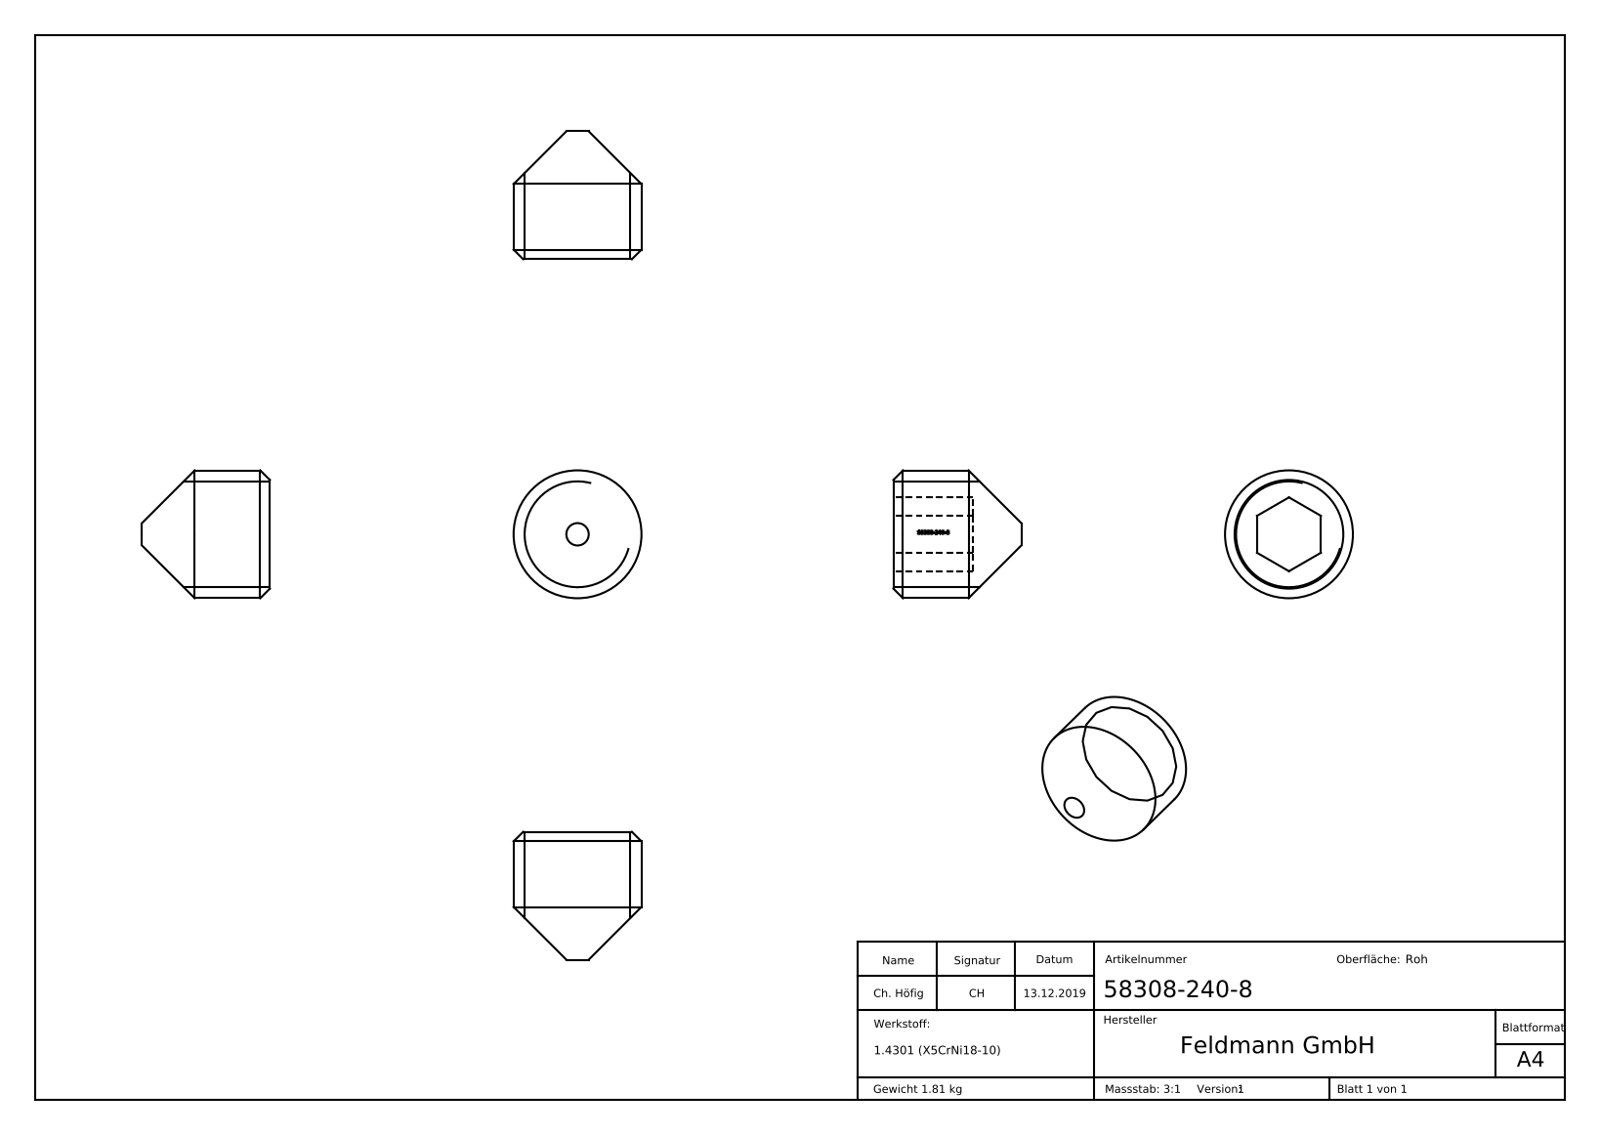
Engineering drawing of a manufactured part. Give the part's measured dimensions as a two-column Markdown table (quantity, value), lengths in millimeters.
| quantity | value |
| --- | --- |
| part name | 58308-240-8 |
| STEP written by | SolidWorks 2015 (CONFIG_CONTROL_DESIGN) |
| units | millimeters |
| bodies | 1 solid, 168 faces (65 planar, 1 cylindrical, 102 other) |
| overall size | 70 × 8 × 8 |
| volume | 229 mm³ |
| surface area | 300 mm² |
| round bosses / shafts (diameter × count) | 8 × 1 |
| main face-to-face distances | 4, 5, 3, 8, 4.1, 5.06, 2.06, 2.94, 5.09, 2.09 |
